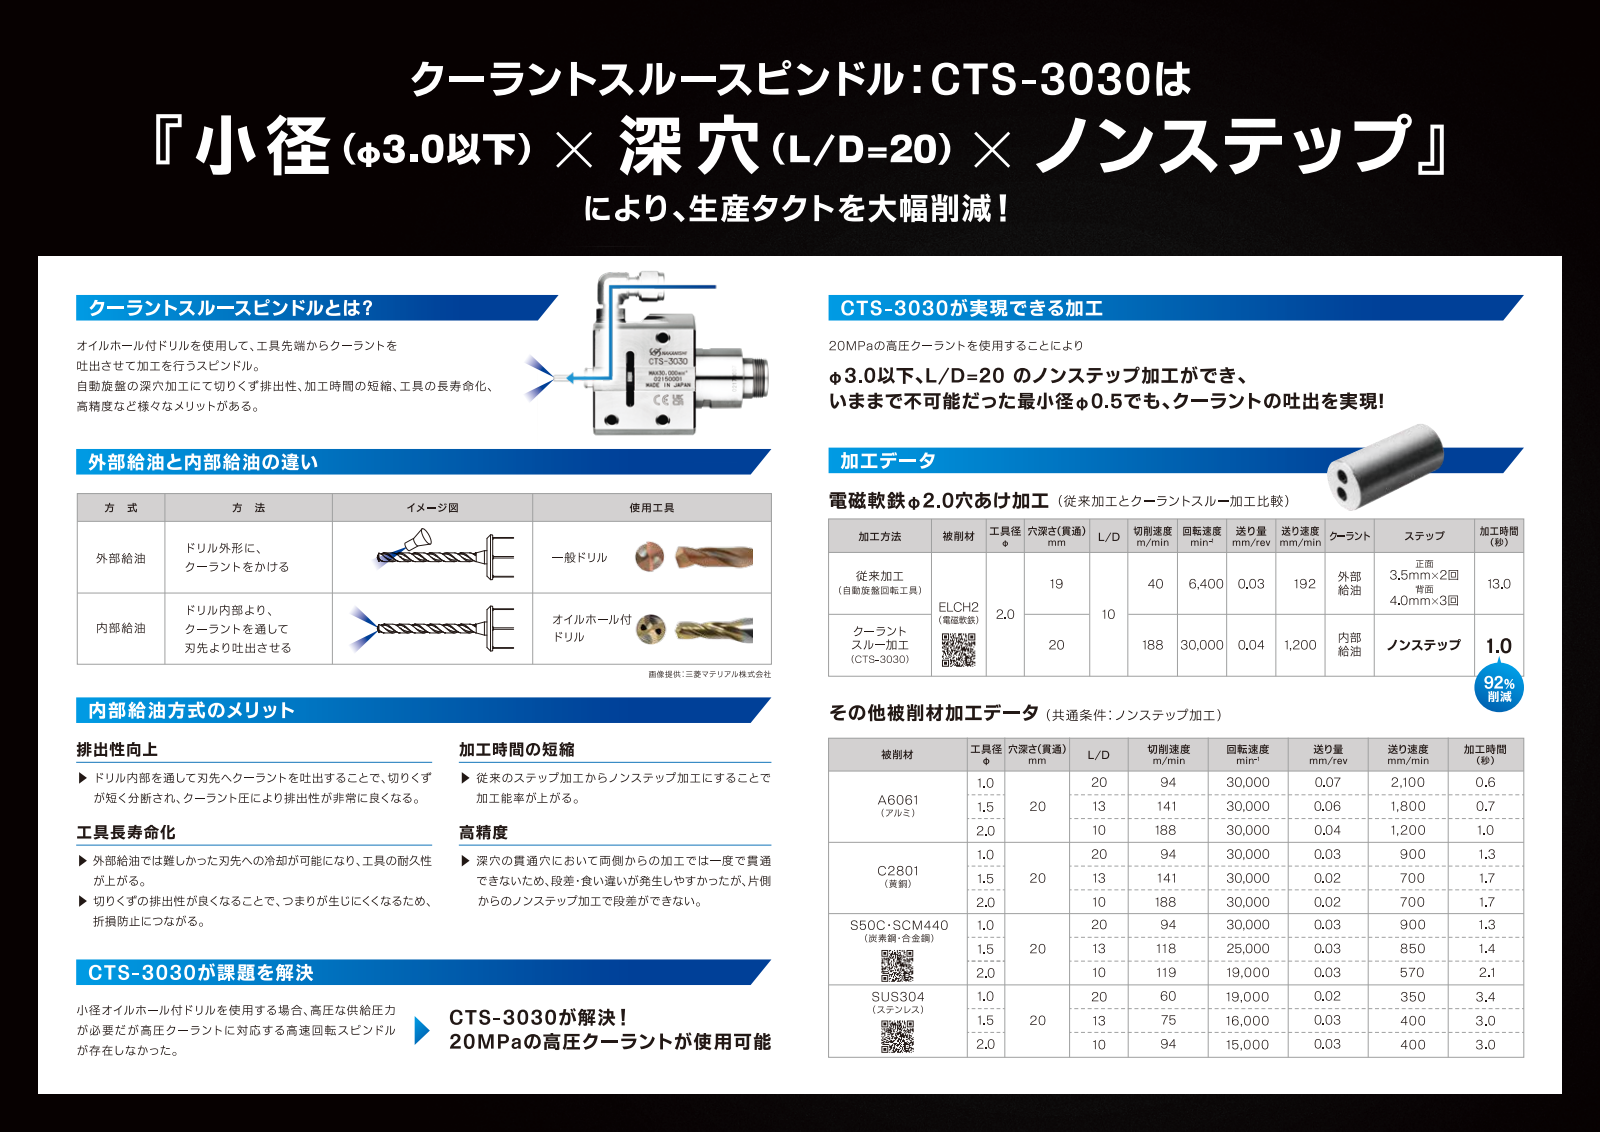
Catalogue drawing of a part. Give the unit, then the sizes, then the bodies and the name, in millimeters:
Units: millimetres
Overall size (bounding box): 90.77 × 81.35 × 43
Round holes (diameter × count): ⌀1.6 ×6, ⌀5.2 ×3, ⌀4 ×2, ⌀6 ×2, ⌀6.5 ×2, ⌀6.8 ×2, ⌀10.5 ×2, ⌀2 ×1, ⌀2.3 ×1, ⌀3.1 ×1, ⌀4.8 ×1, ⌀5 ×1
Round bosses / shafts (diameter × count): ⌀36.9 ×1, ⌀30 ×1, ⌀20.5 ×1, ⌀20.2 ×1, ⌀19.8 ×1, ⌀18.5 ×1, ⌀15.24 ×1, ⌀13.97 ×1
Partial cylindrical surfaces — rounded edges, fillets, slot ends (radius × count): R1.5 ×10, R1.1 ×4, R6.35 ×1, R32.25 ×1
Main face-to-face distances: 43, 50, 1.5, 41.5, 1.36, 48.64, 40, 55, 19.8, 18.44
Hole centre spacings: 16.8, 19.3, 23.76, 7.3, 9.5, 13.87, 17.1, 20.27
Volume: 77 796 mm³ · Surface area: 40 041 mm²
Bodies: 12 solids, 664 faces (299 planar, 184 cylindrical, 181 other)
Part name (STEP PRODUCT): CTS-3030
STEP written by: SolidWorks 2017 (CONFIG_CONTROL_DESIGN)
